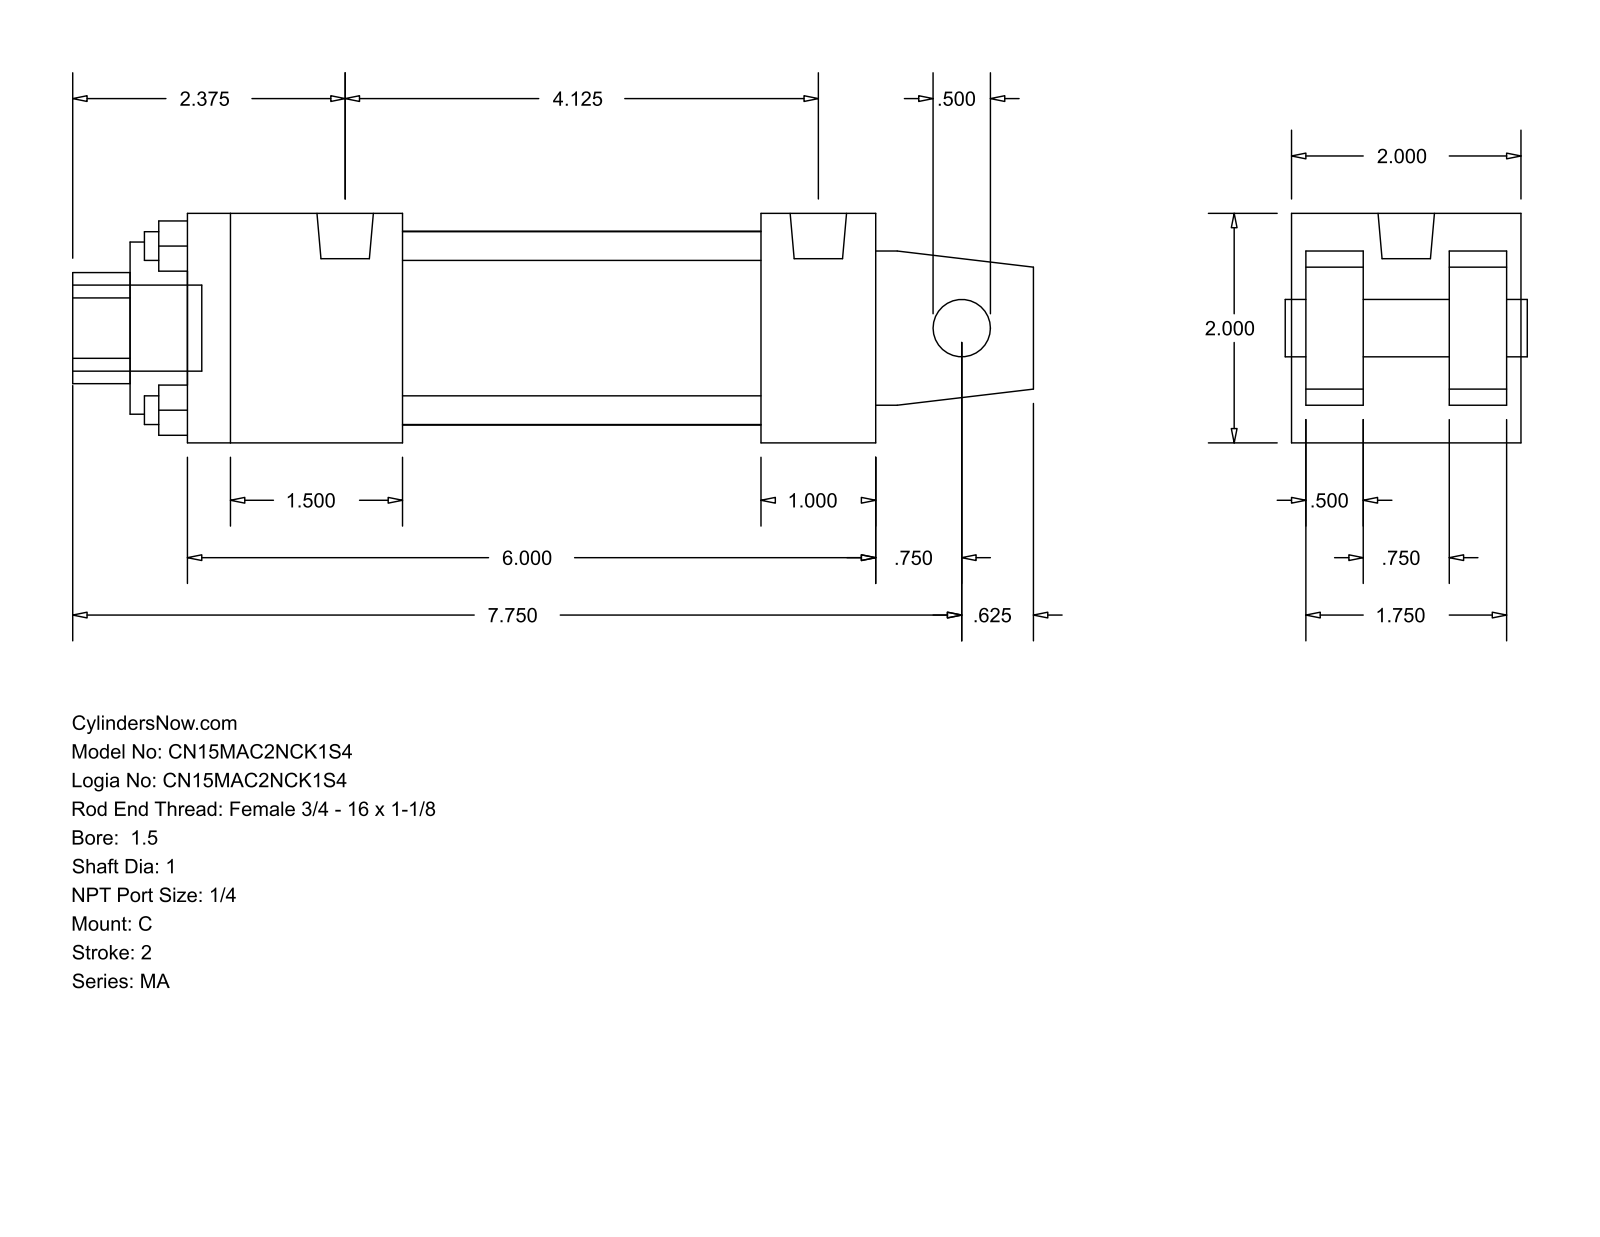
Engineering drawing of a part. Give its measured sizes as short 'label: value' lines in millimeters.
name: MA_C__0150_1
written by: GSSL Pune (CONFIG_CONTROL_DESIGN)
unit: mm
bodies: 0 solids, 103 faces (76 planar, 27 cylindrical, 0 other)
size: 212.72 × 50.8 × 50.8
holes: 4× ⌀6.35, 1× ⌀12.7, 1× ⌀25.4, 1× ⌀38.1, 1× ⌀42.93
bosses: 4× ⌀7.94, 2× ⌀12.49, 1× ⌀19.05
rounds: 1× R12.29
face distances: 50.8, 47.63, 12.7, 3.17, 15.87, 34.93, 31.76, 44.46, 152.4, 25.4
hole spacings: 25.68, 36.32, 51.36
